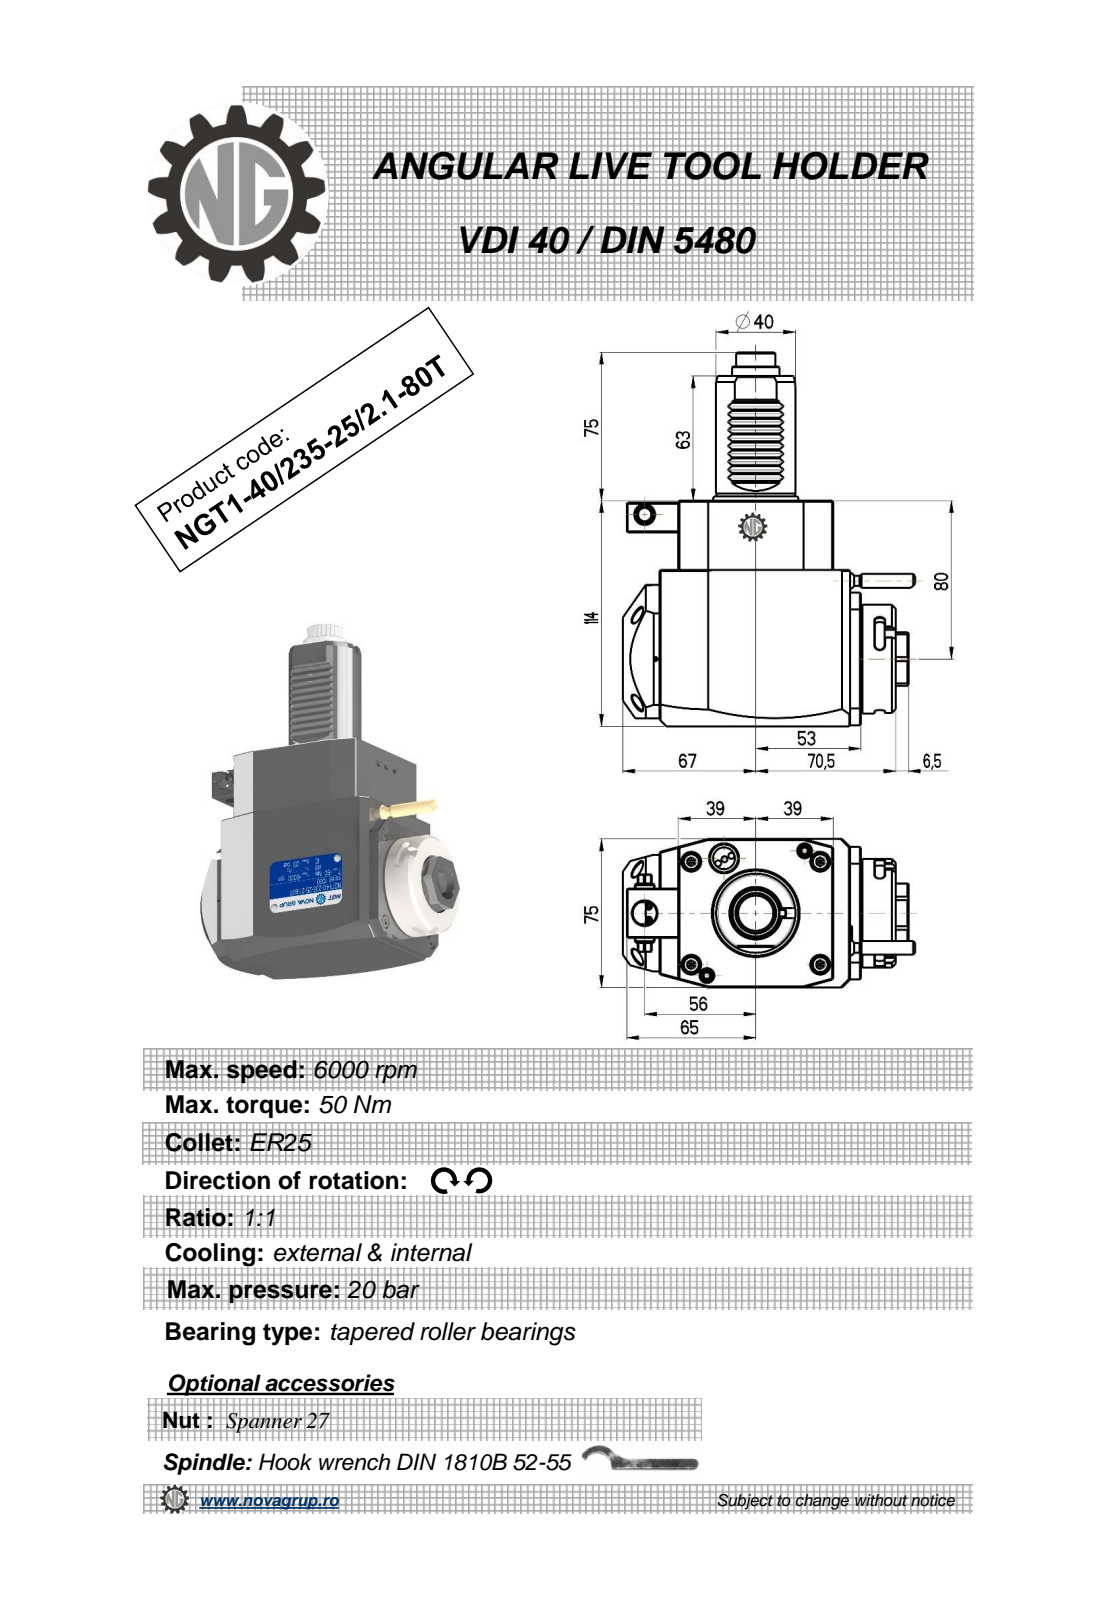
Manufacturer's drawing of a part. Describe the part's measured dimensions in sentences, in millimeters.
The part is named "NGT1_40_235_25_1_1_80T". Its 3-D file was written by "PRO/ENGINEER BY PARAMETRIC TECHNOLOGY CORPORATION, 2010280 (CONFIG_CONTROL_DESIGN)". It is 1 solid with 458 faces: 186 planar, 178 cylindrical and 94 other. Overall it measures 189 by 147.33 by 75 millimeters. Its volume is 959 766 cubic millimeters and its surface area 71 151 square millimeters. Round holes: 1 of diameter 2.5, 1 of diameter 3, 1 of diameter 9.5, 1 of diameter 12, 1 of diameter 18. Round bosses or shafts: 2 of diameter 8, 1 of diameter 55, 1 of diameter 48, 1 of diameter 40, 1 of diameter 24, 1 of diameter 10, 1 of diameter 7, 1 of diameter 5. Partial cylindrical surfaces (rounded edges, fillets, slot ends): 48 of radius 2.08, 10 of radius 0.3, 6 of radius 2.5, 2 of radius 15, 2 of radius 180, 1 of radius 3.85, 1 of radius 4.25, 1 of radius 9.08. The main face-to-face distances are 75, 114, 14, 109.5, 78, 92, 17.5, 31.5, 79, 28. The hole center spacings are 36.47, 43.2, 71.5.
